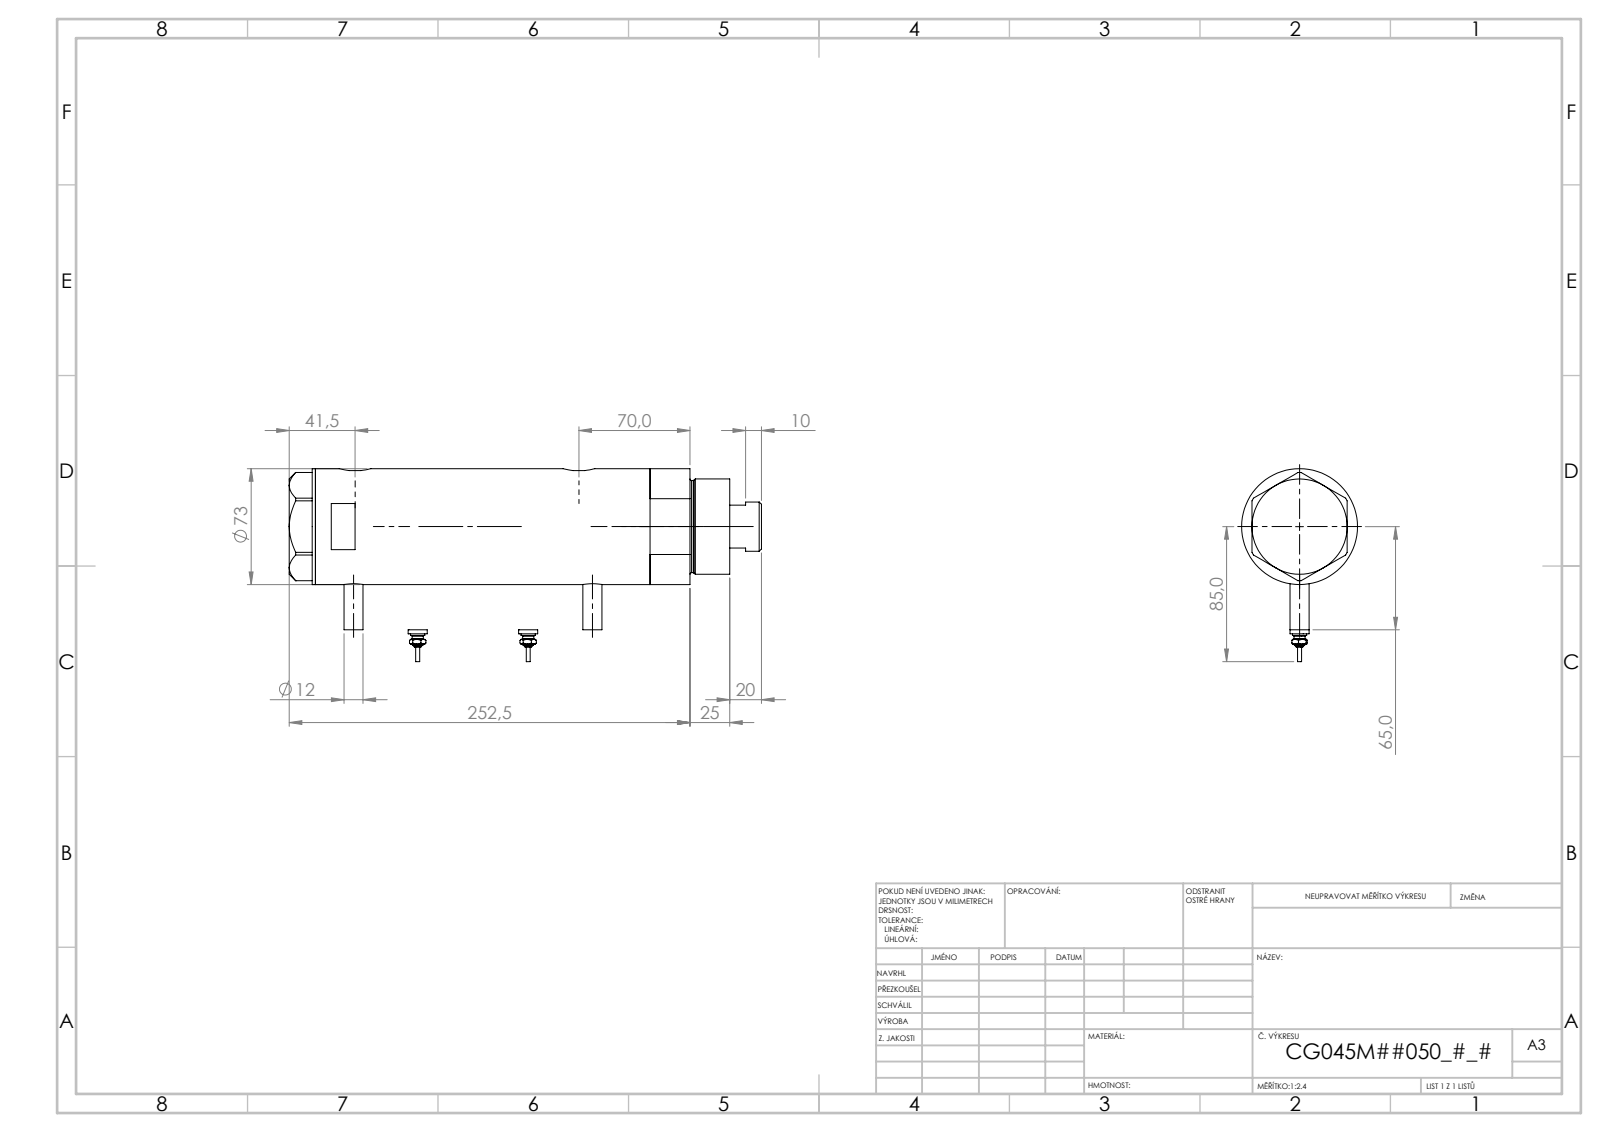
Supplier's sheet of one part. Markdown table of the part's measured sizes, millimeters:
| quantity | value |
| --- | --- |
| part name | V270CG_BACK; V270CG_FRONT; V270CG_MIDDLE; V270CG_SWITCH (+1 more) |
| STEP written by | SolidWorks 2019 (CONFIG_CONTROL_DESIGN) |
| units | millimeters |
| bodies | 6 solids, 231 faces (78 planar, 79 cylindrical, 74 other) |
| overall size | 241.52 × 105.3 × 73 |
| volume | 839 572 mm³ |
| surface area | 145 449 mm² |
| round holes (diameter × count) | 5 × 2, 12.5 × 2, 13.16 × 2, 10.5 × 1, 32 × 1, 33.5 × 1, 45 × 1, 48 × 1, 64 × 1 |
| round bosses / shafts (diameter × count) | 12 × 3, 9 × 2, 7 × 2, 4.34 × 2, 2.4 × 2, 73 × 1, 60 × 1, 58 × 1 |
| partial cylindrical surfaces (radius × count) | 10 × 2 |
| main face-to-face distances | 117.14, 26, 91.14, 16.5, 42.5, 133.64, 205.01, 221.51, 179.01, 87.87 |
| hole center spacings | 101.65, 0.99, 1, 8.5, 8.51, 92.15, 93.14, 93.15 |
